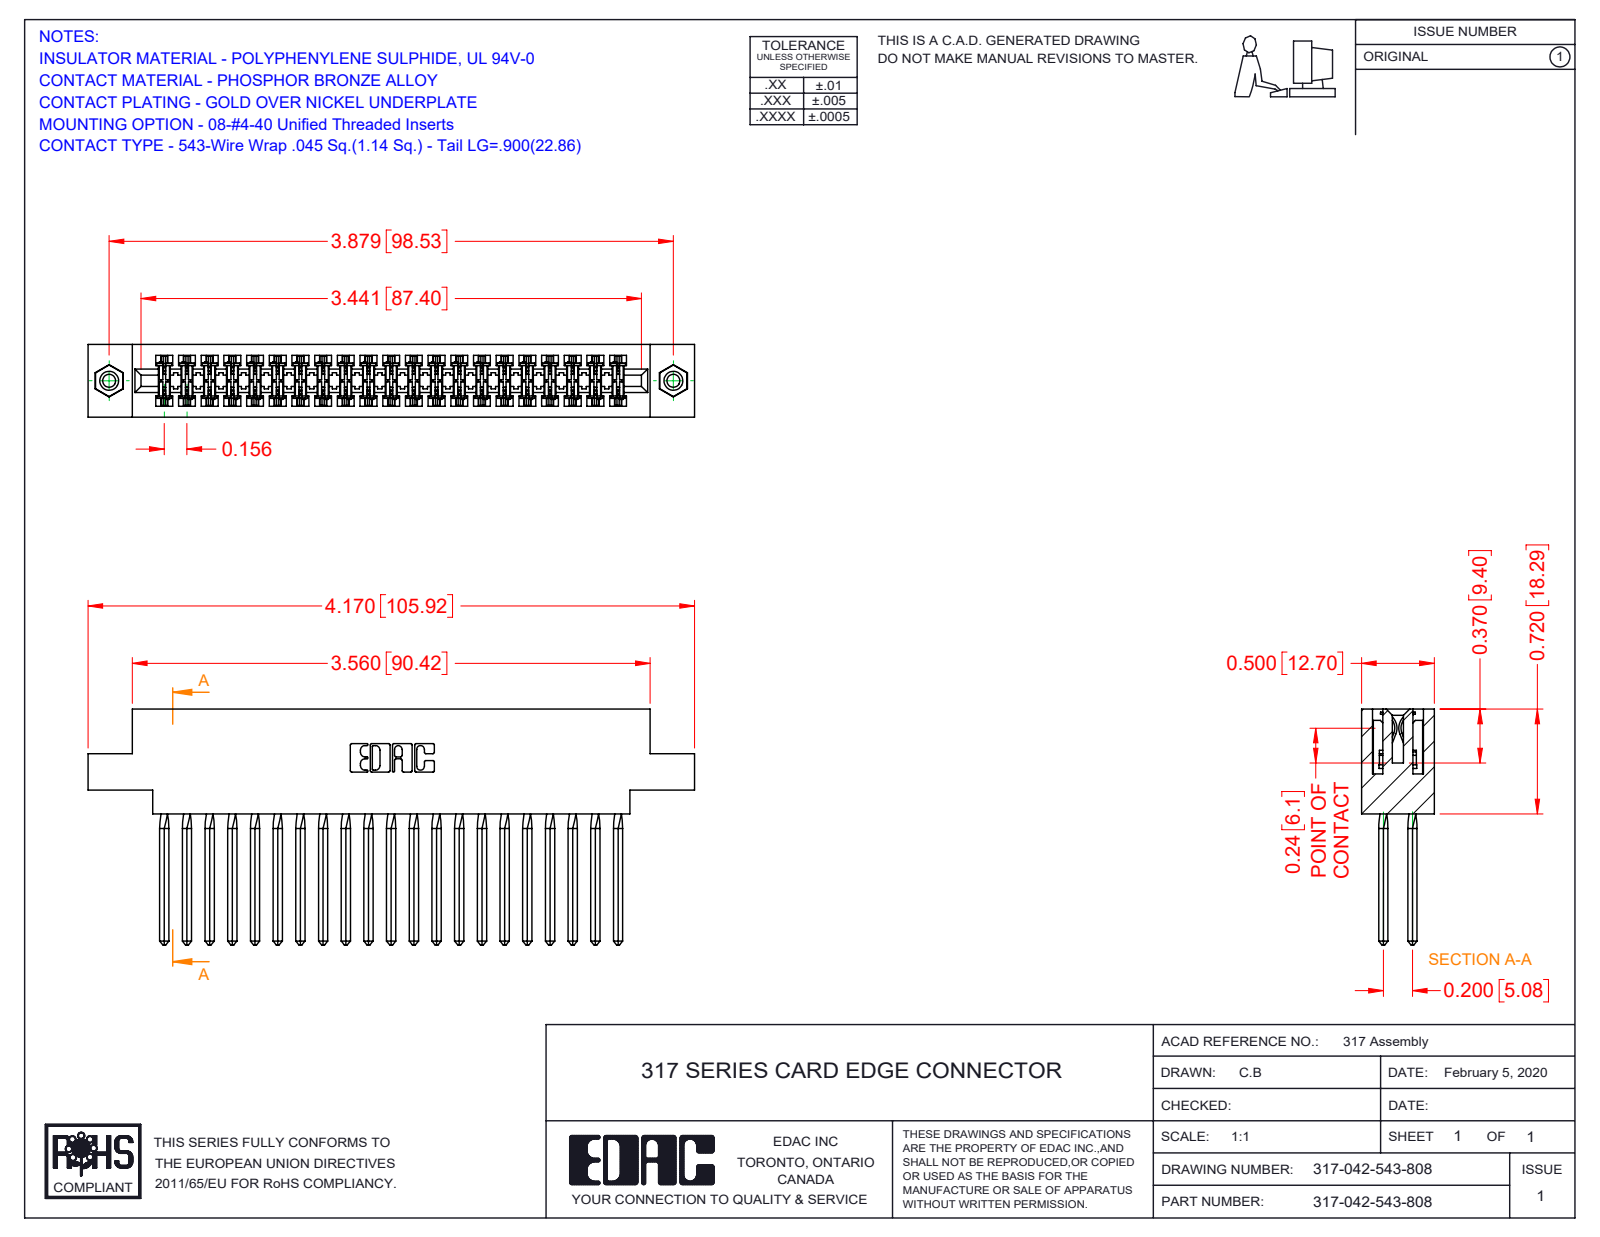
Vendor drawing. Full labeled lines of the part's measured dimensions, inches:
Part name (STEP PRODUCT): 317 Part_.156 Dia - TI; 345-250-001_345-250-003-102; 317-042-543-878; 317-290-001_543
STEP written by: SolidWorks 2016 (CONFIG_CONTROL_DESIGN)
Units: inches
Bodies: 45 solids, 3900 faces (3156 planar, 560 cylindrical, 184 other)
Overall size (bounding box): 4.17 × 1.62 × 0.5
Volume: 1.054 in³ · Surface area: 39.36 in²
Round holes (diameter × count): ⌀0.089 ×2, ⌀0.125 ×2, ⌀0.156 ×2
Round bosses / shafts (diameter × count): ⌀0.155 ×2
Partial cylindrical surfaces — rounded edges, fillets, slot ends (radius × count): R0.015 ×84, R0.01 ×22, R0.007 ×6, R0.031 ×6, R0.026 ×3, R0.095 ×2, R0.1 ×2, R0.11 ×2
Main face-to-face distances: 0.5, 0.075, 0.425, 0.11, 0.35, 0.22, 0.195, 0.72, 0.094, 0.2
Hole centre spacings: 3.879
